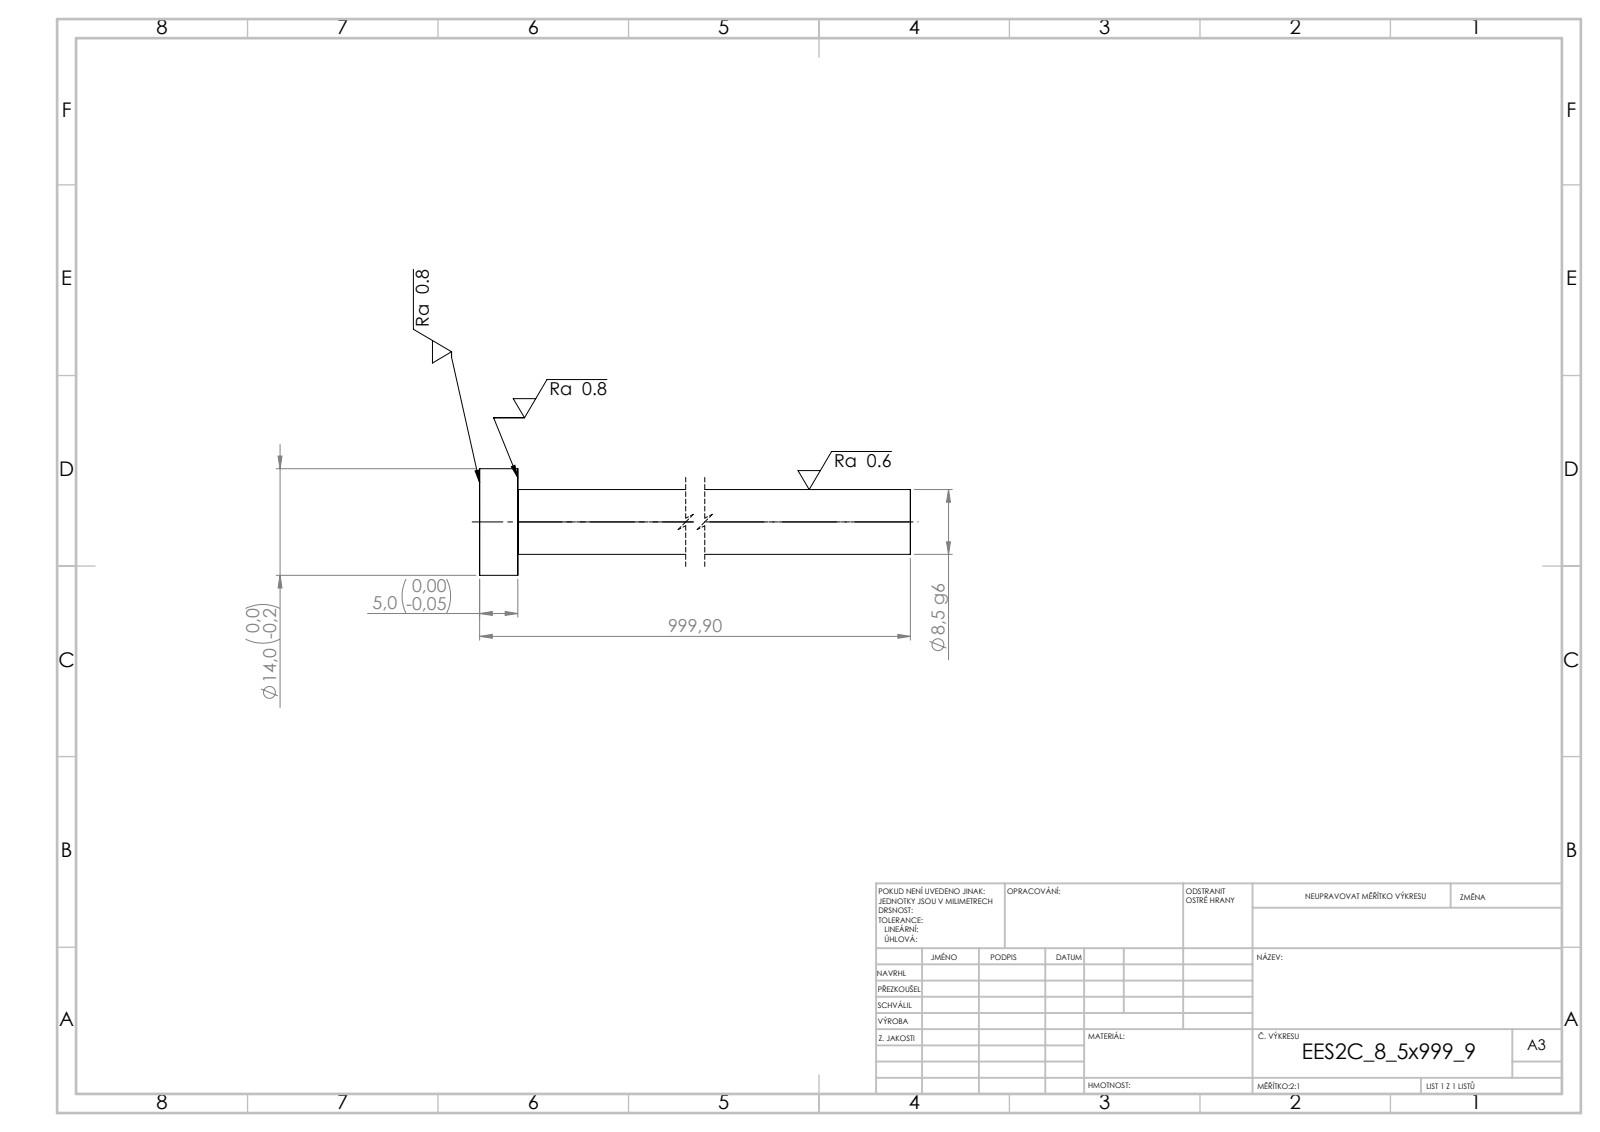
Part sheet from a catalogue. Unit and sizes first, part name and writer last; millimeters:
Units: millimetres
Overall size (bounding box): 999.9 × 14 × 14
Round bosses / shafts (diameter × count): ⌀14 ×1, ⌀8.5 ×1
Main face-to-face distances: 5, 999.9, 994.9
Volume: 57 225 mm³ · Surface area: 27 095 mm²
Bodies: 1 solid, 7 faces (3 planar, 4 cylindrical, 0 other)
STEP written by: SolidWorks 2019 (CONFIG_CONTROL_DESIGN)
